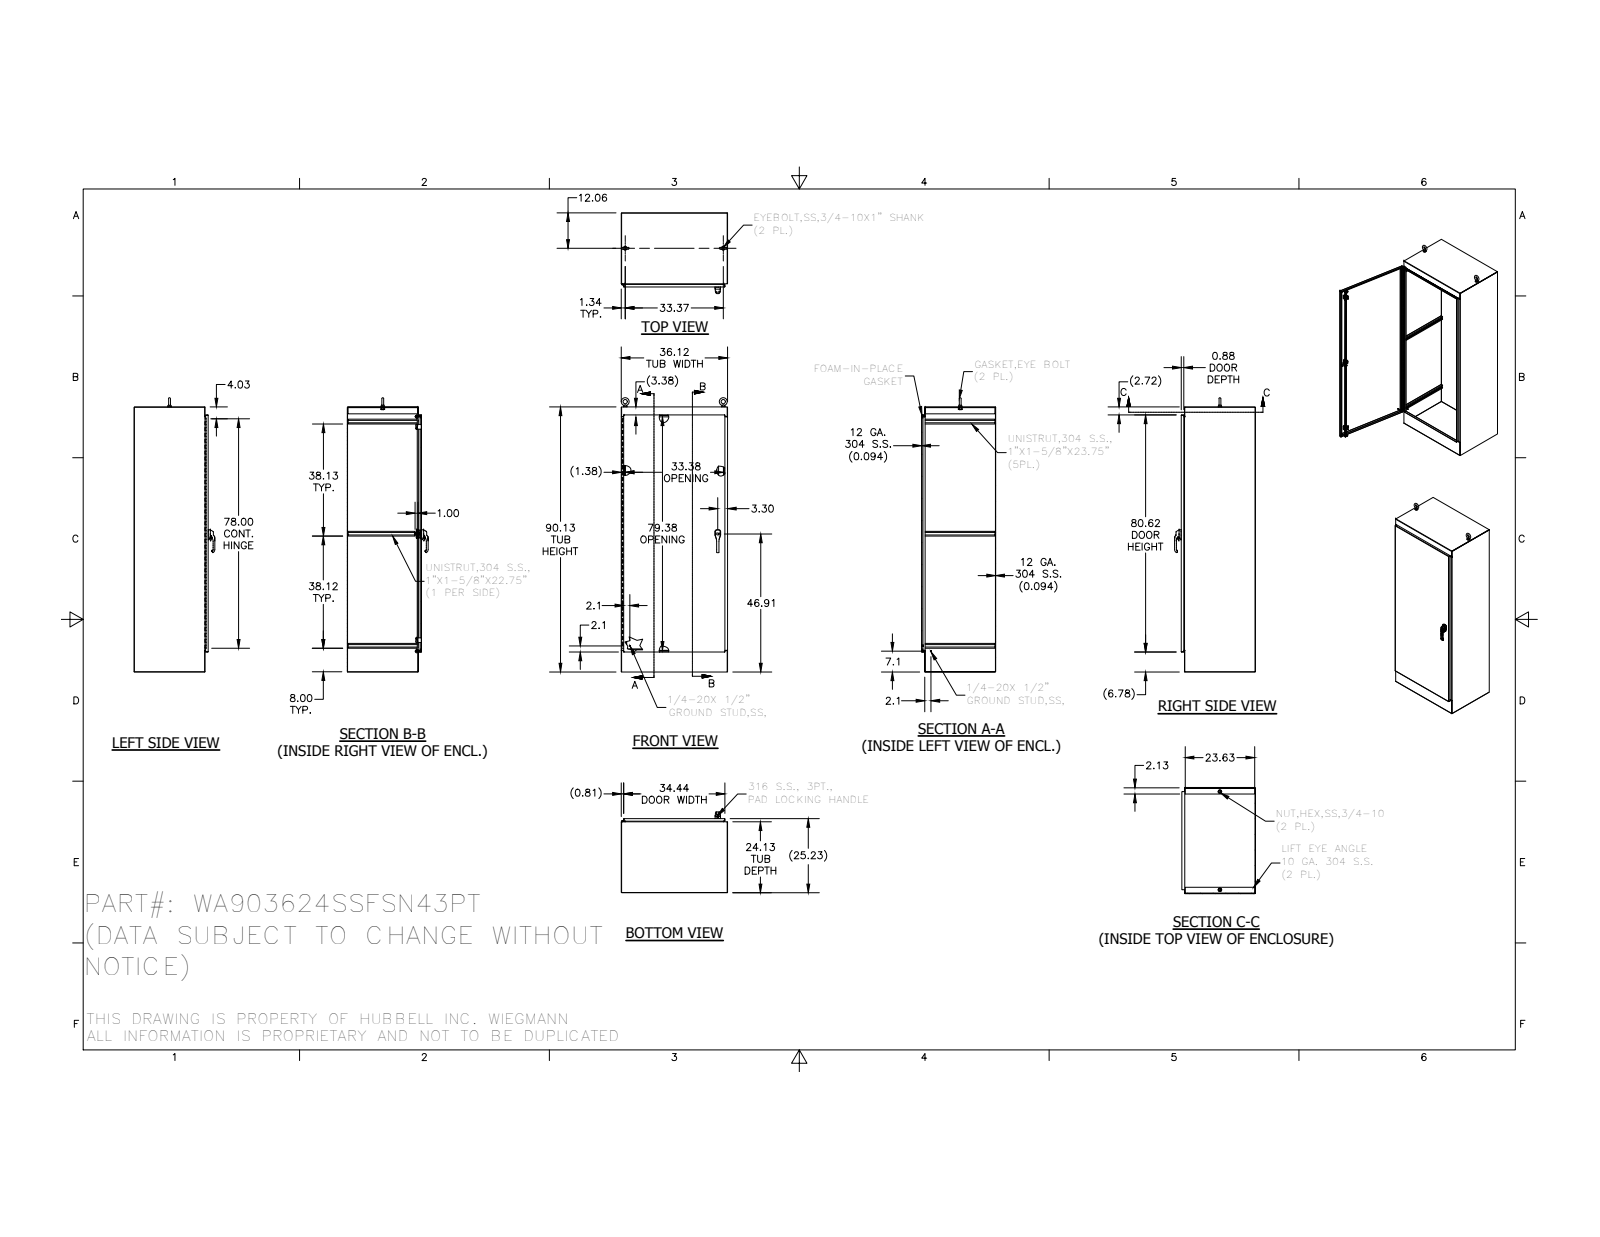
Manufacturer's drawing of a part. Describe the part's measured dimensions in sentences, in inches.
The part is named "WA9024SSFSN43PT-LS; 3862; HFW369101; HFW3026 (+8 more)". Its 3-D file was written by "SolidWorks 2014 (AUTOMOTIVE_DESIGN)". It is 66 solids with 3601 faces: 1309 planar, 1352 cylindrical and 940 other. Overall it measures 93.248 by 36.125 by 27.476 inches. Its volume is 1 401 cubic inches and its surface area 29 156 square inches. Round holes: 8 of diameter 0.262, 8 of diameter 0.375, 4 of diameter 0.187, 3 of diameter 0.213, 3 of diameter 0.25, 3 of diameter 0.28, 2 of diameter 0.165, 2 of diameter 0.241, 2 of diameter 0.252, 2 of diameter 0.315, 2 of diameter 0.4, 2 of diameter 0.402. Round bosses or shafts: 3 of diameter 1, 3 of diameter 0.236, 2 of diameter 1.25, 2 of diameter 1.12, 2 of diameter 0.75, 2 of diameter 0.563, 2 of diameter 0.533, 2 of diameter 0.531. Partial cylindrical surfaces (rounded edges, fillets, slot ends): 180 of radius 0.02, 107 of radius 0.012, 26 of radius 0.125, 23 of radius 0.019, 19 of radius 0.05, 17 of radius 0.031, 14 of radius 0.079, 13 of radius 0.125. The main face-to-face distances are 0.094, 25.133, 36.031, 25.039, 25.227, 35.937, 36.125, 90.031, 24.031, 1.102. The hole center spacings are 8.667, 26, 0.38, 0.76, 1.102, 1.714, 2.763, 17.333.
